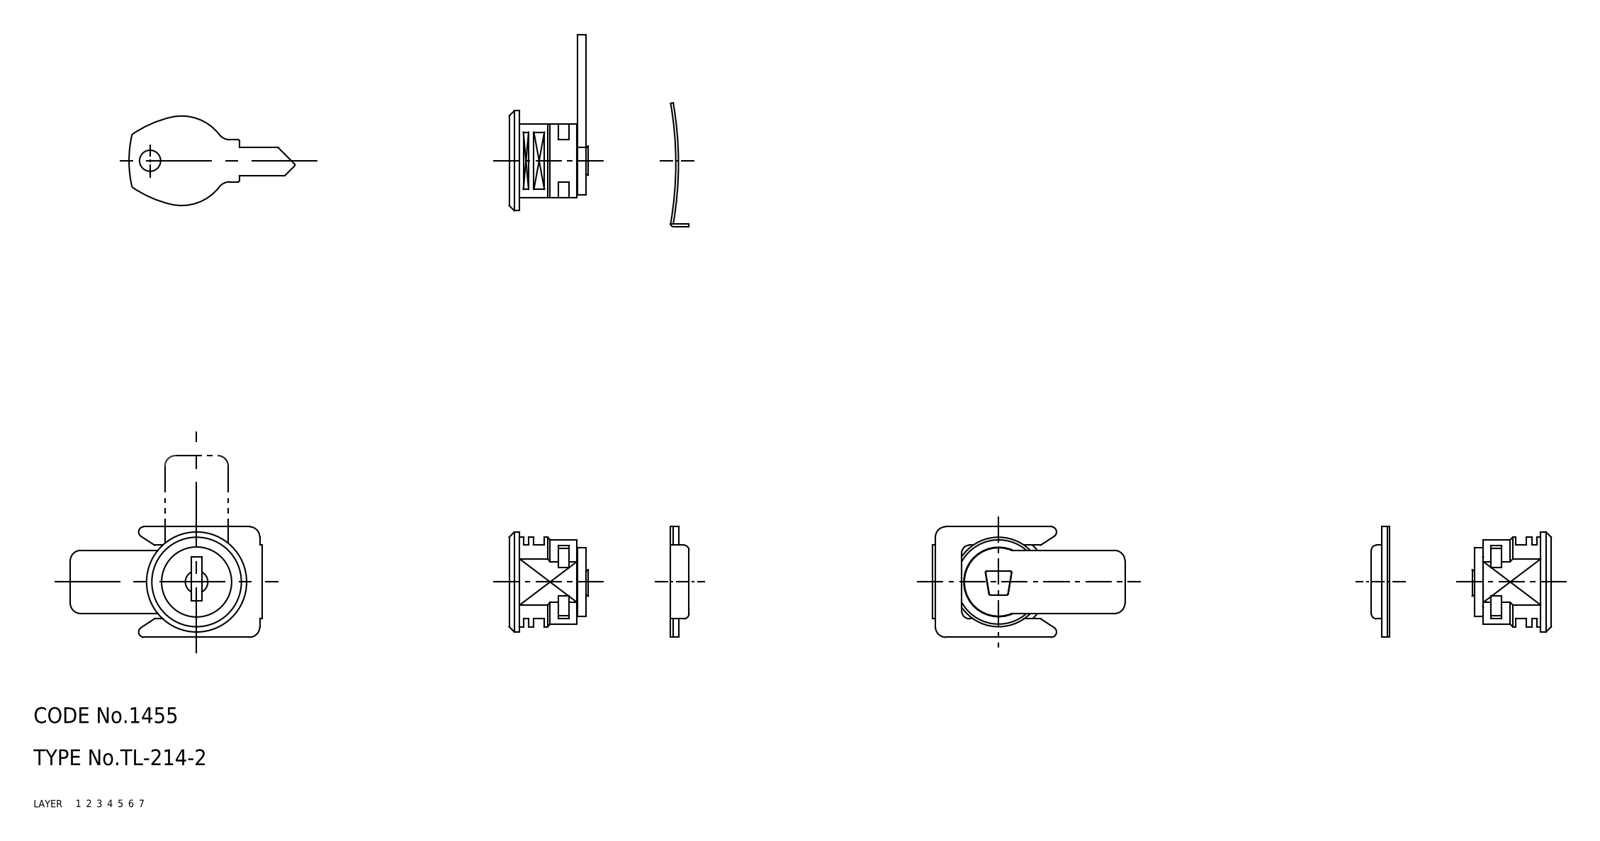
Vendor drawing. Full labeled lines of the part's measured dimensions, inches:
Part name (STEP PRODUCT): retainer; lock; key; cam (+1 more)
STEP written by: CADfix (AUTOMOTIVE_DESIGN)
Units: inches
Bodies: 5 solids, 112 faces (0 planar, 0 cylindrical, 112 other)
Overall size (bounding box): 2.667 × 1.437 × 0.827
Volume: 0.235 in³ · Surface area: 7.128 in²
